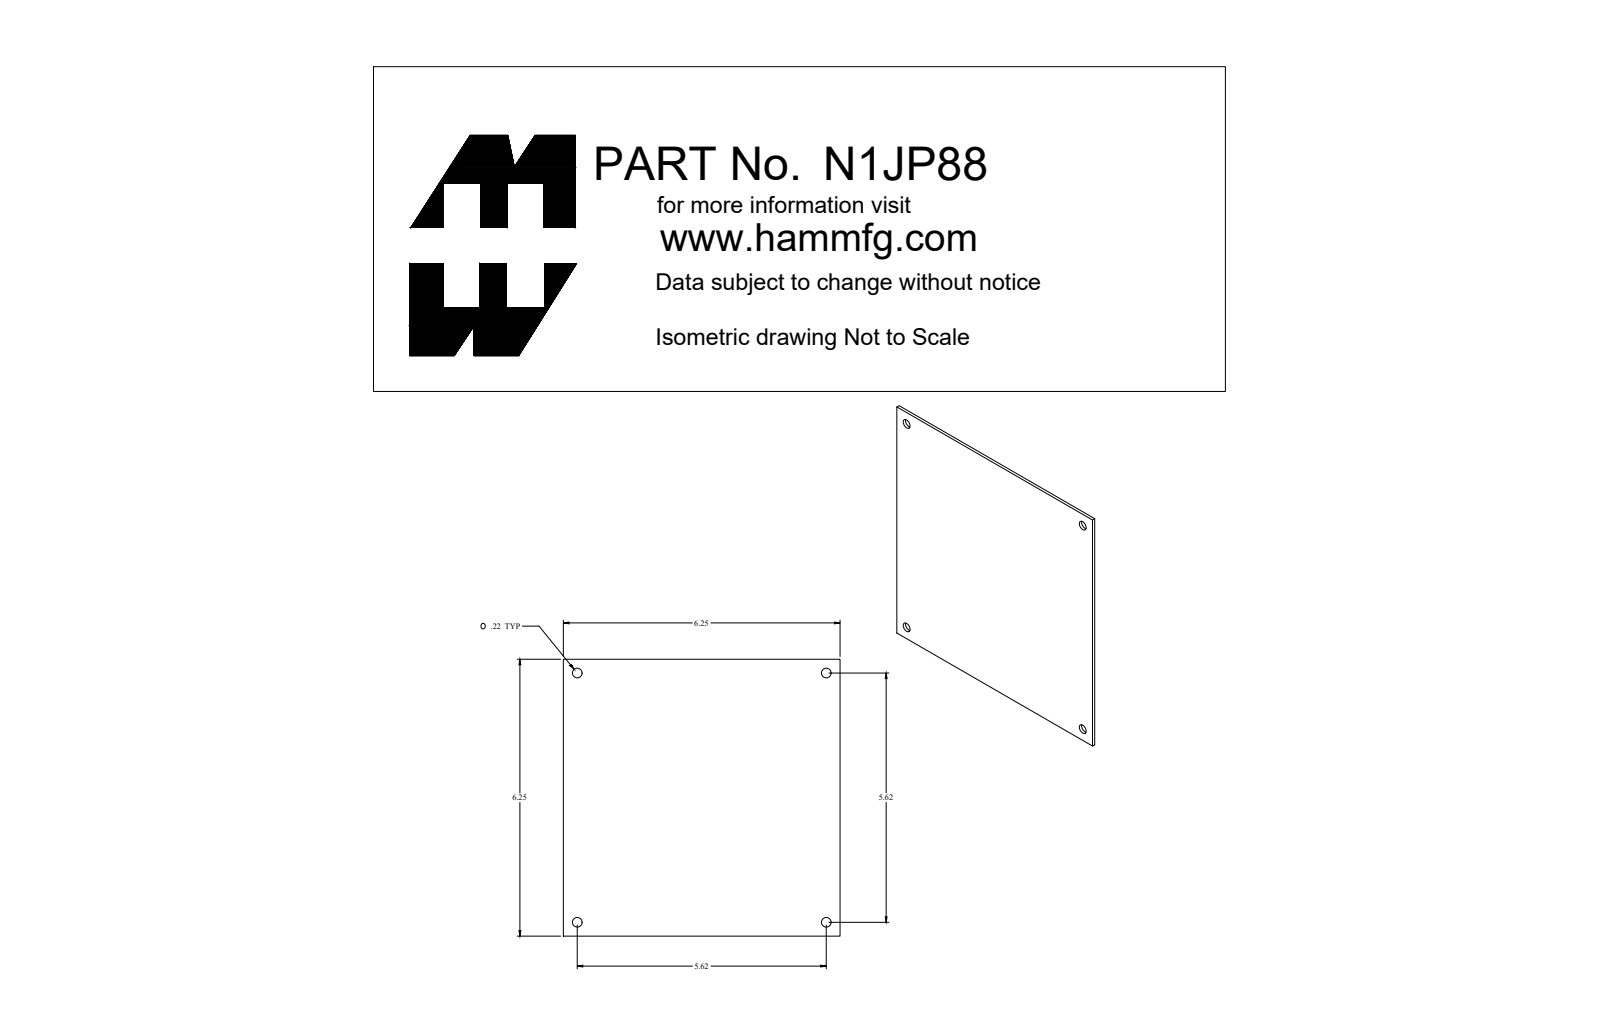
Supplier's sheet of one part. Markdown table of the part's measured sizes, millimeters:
| quantity | value |
| --- | --- |
| part name | N1JP88 |
| STEP written by | SolidWorks 2018 (AUTOMOTIVE_DESIGN) |
| units | millimeters |
| bodies | 1 solid, 18 faces (6 planar, 12 cylindrical, 0 other) |
| overall size | 158.8 × 158.8 × 1.8 |
| volume | 45 820 mm³ |
| surface area | 51 410 mm² |
| round holes (diameter × count) | 6.7 × 4 |
| partial cylindrical surfaces (radius × count) | 3.2 × 4 |
| main face-to-face distances | 1.8, 158.8 |
| hole center spacings | 142.9, 202.1 |
